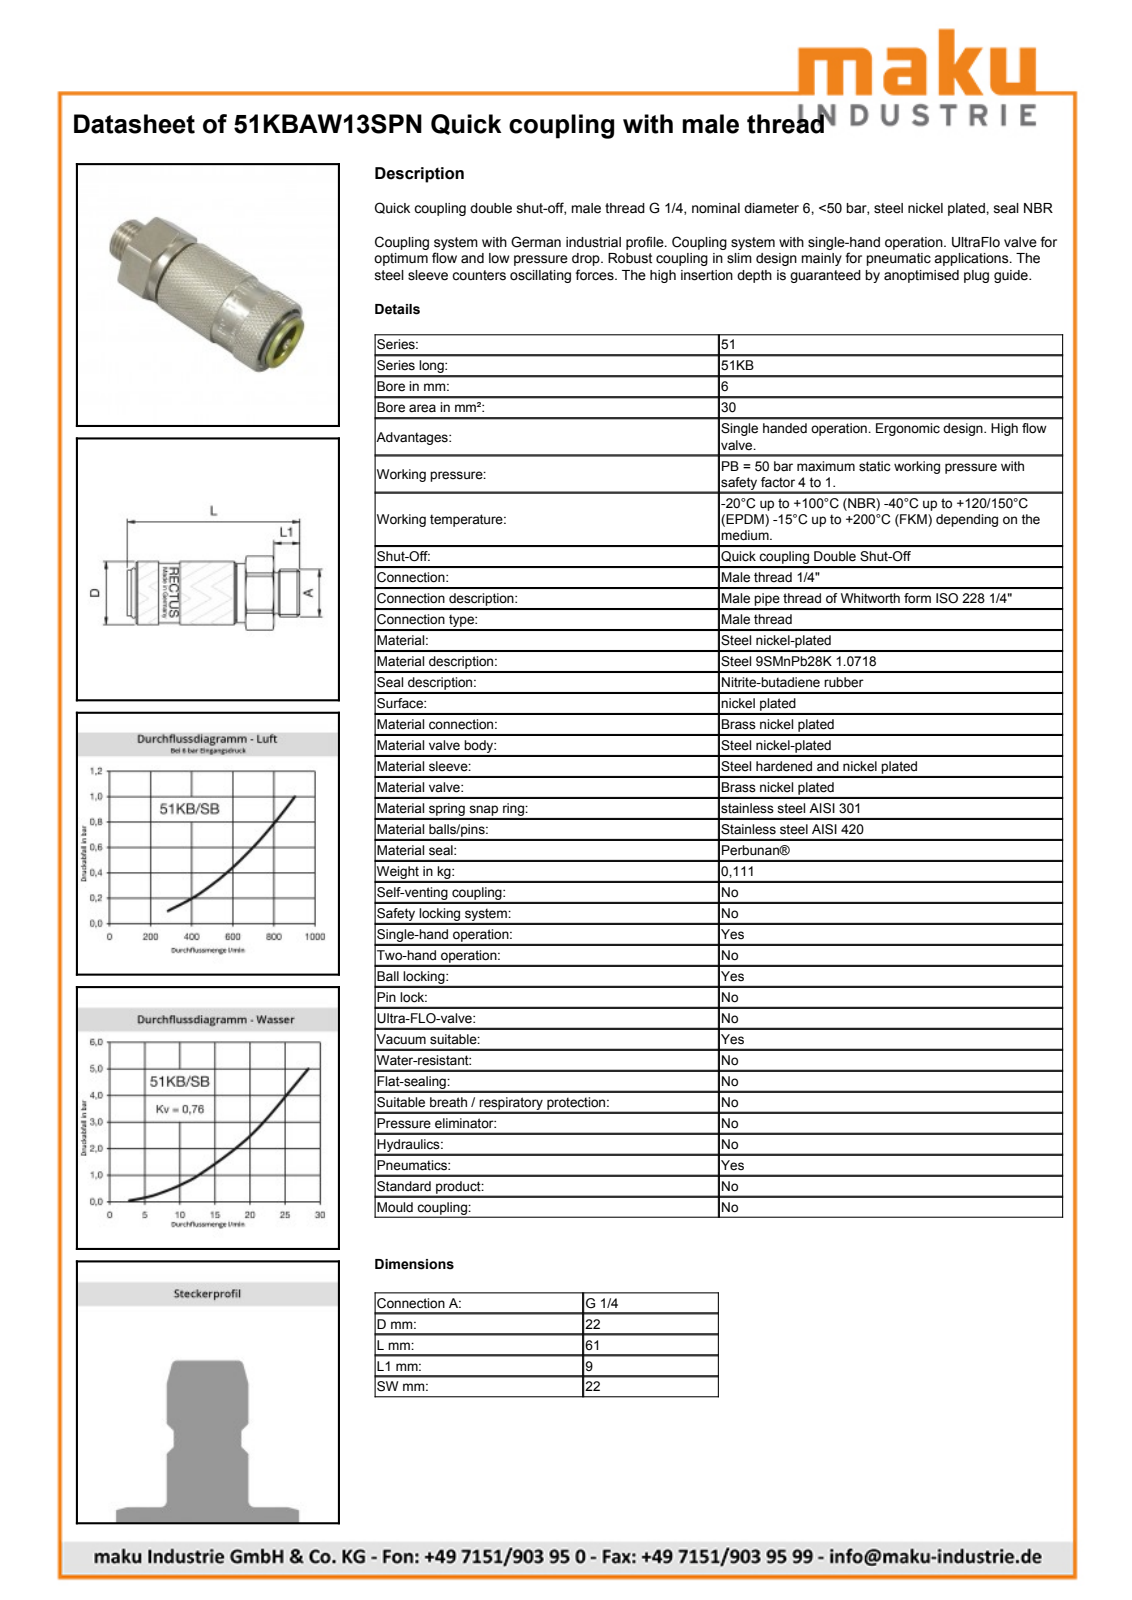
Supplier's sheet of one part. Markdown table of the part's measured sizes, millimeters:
| quantity | value |
| --- | --- |
| part name | D112754 |
| STEP written by | Autodesk Inventor 2013 (AUTOMOTIVE_DESIGN) |
| units | millimeters |
| bodies | 2 solids, 513 faces (166 planar, 70 cylindrical, 277 other) |
| overall size | 59 × 24.64 × 23.52 |
| volume | 18 489 mm³ |
| surface area | 9 646 mm² |
| round holes (diameter × count) | 16.25 × 1, 18.25 × 1, 19.1 × 1, 19.3 × 1, 19.75 × 1 |
| round bosses / shafts (diameter × count) | 22.15 × 1, 21 × 1, 20.9 × 1, 19 × 1, 18 × 1, 16 × 1, 14.57 × 1, 13.16 × 1 |
| partial cylindrical surfaces (radius × count) | 7.54 × 1, 10.4 × 1, 12.4 × 1 |
| main face-to-face distances | 22, 49.9, 3, 11, 59, 9.1, 46.9, 56, 19.5, 14 |
